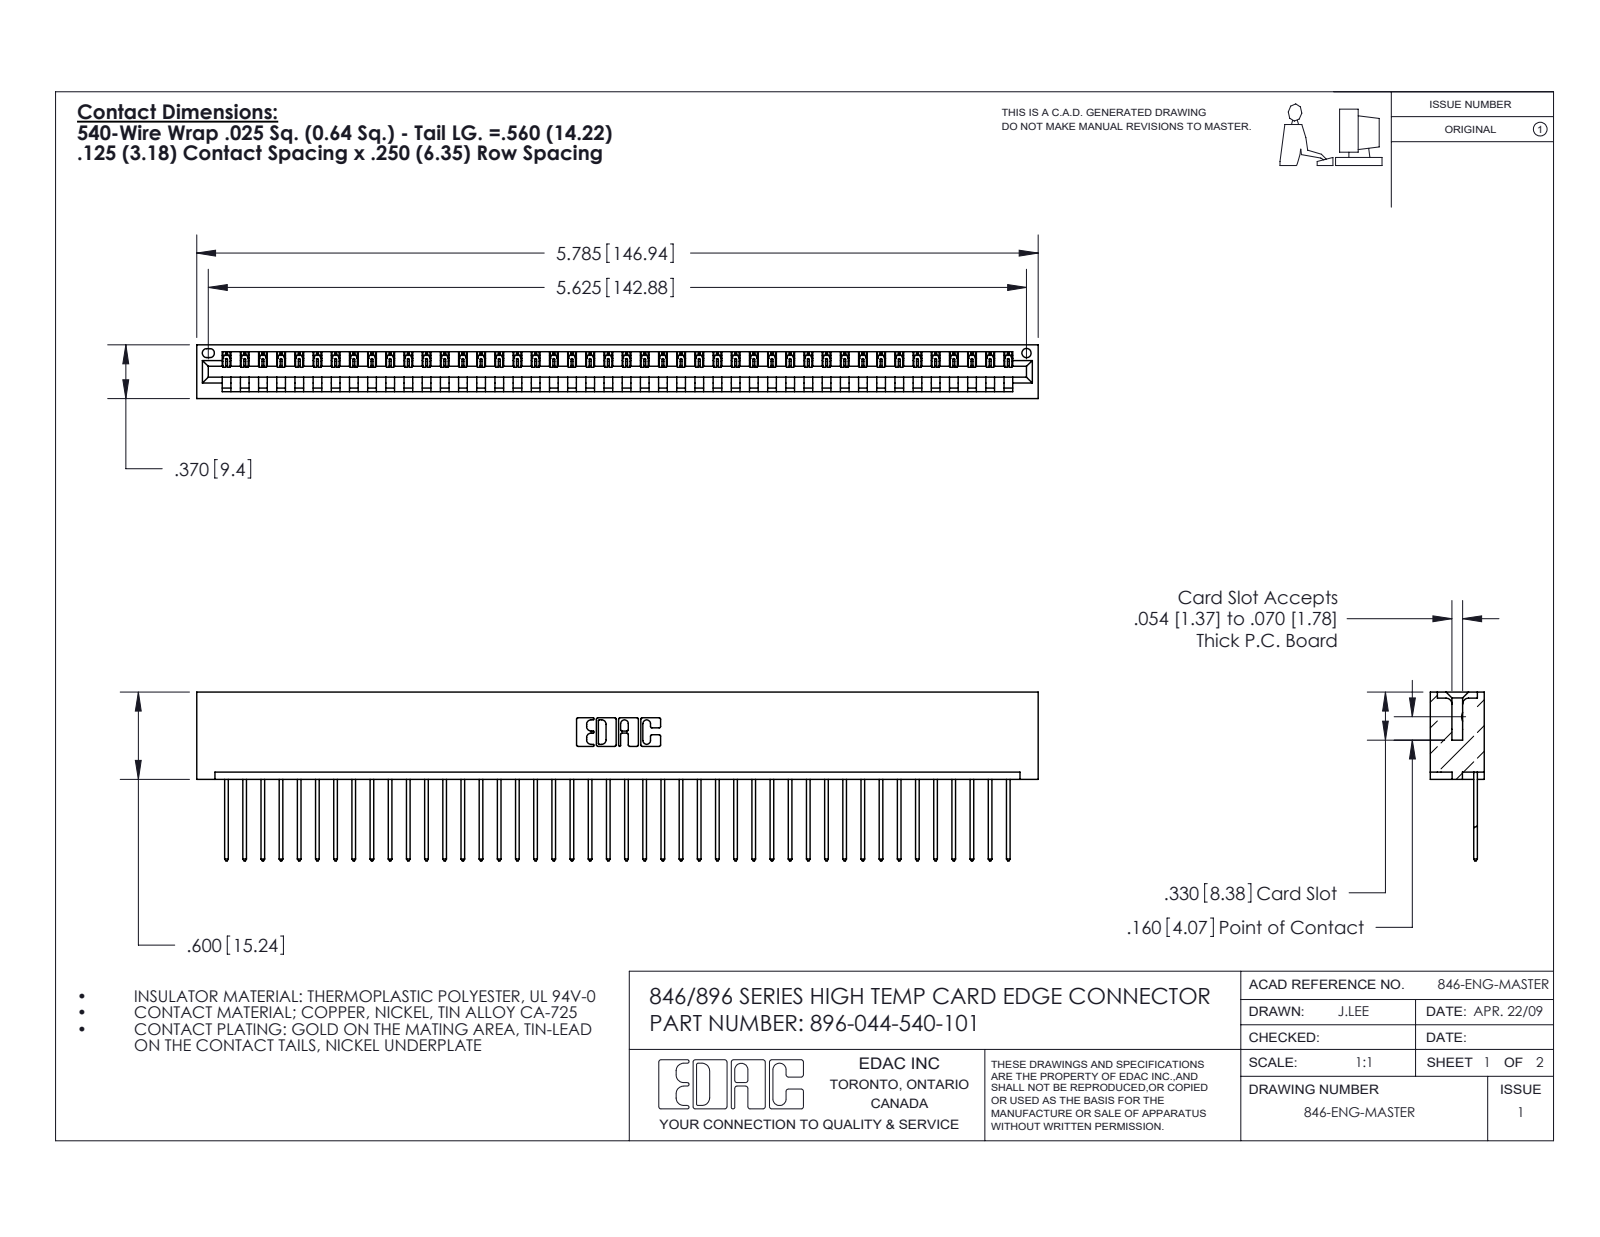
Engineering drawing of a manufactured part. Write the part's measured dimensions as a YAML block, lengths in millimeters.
part_name: "345-292-001_345-293-140; 396-044-540-101; 346 Part_No Mounting Lugs"
step_written_by: "SolidWorks 2016 (CONFIG_CONTROL_DESIGN)"
units: millimeters
bodies: {solids: 45, faces: 2666, planar: 1832, cylindrical: 834, other: 0}
overall_size: [146.9, 29.5, 9.4]
volume: 14700
surface_area: 18890
round_holes:
  - {diameter: 1.6, count: 1}
partial_cylinders:
  - {radius: 0.2, count: 88}
  - {radius: 0.3, count: 88}
  - {radius: 0.3, count: 22}
  - {radius: 0.2, count: 6}
  - {radius: 0.8, count: 6}
  - {radius: 0.7, count: 3}
  - {radius: 0.8, count: 2}
  - {radius: 1, count: 2}
face_to_face_distances: [1.2, 8.2, 9.4, 6.4, 1.8, 7.6, 0.6, 3.8, 5.6, 2.5]
